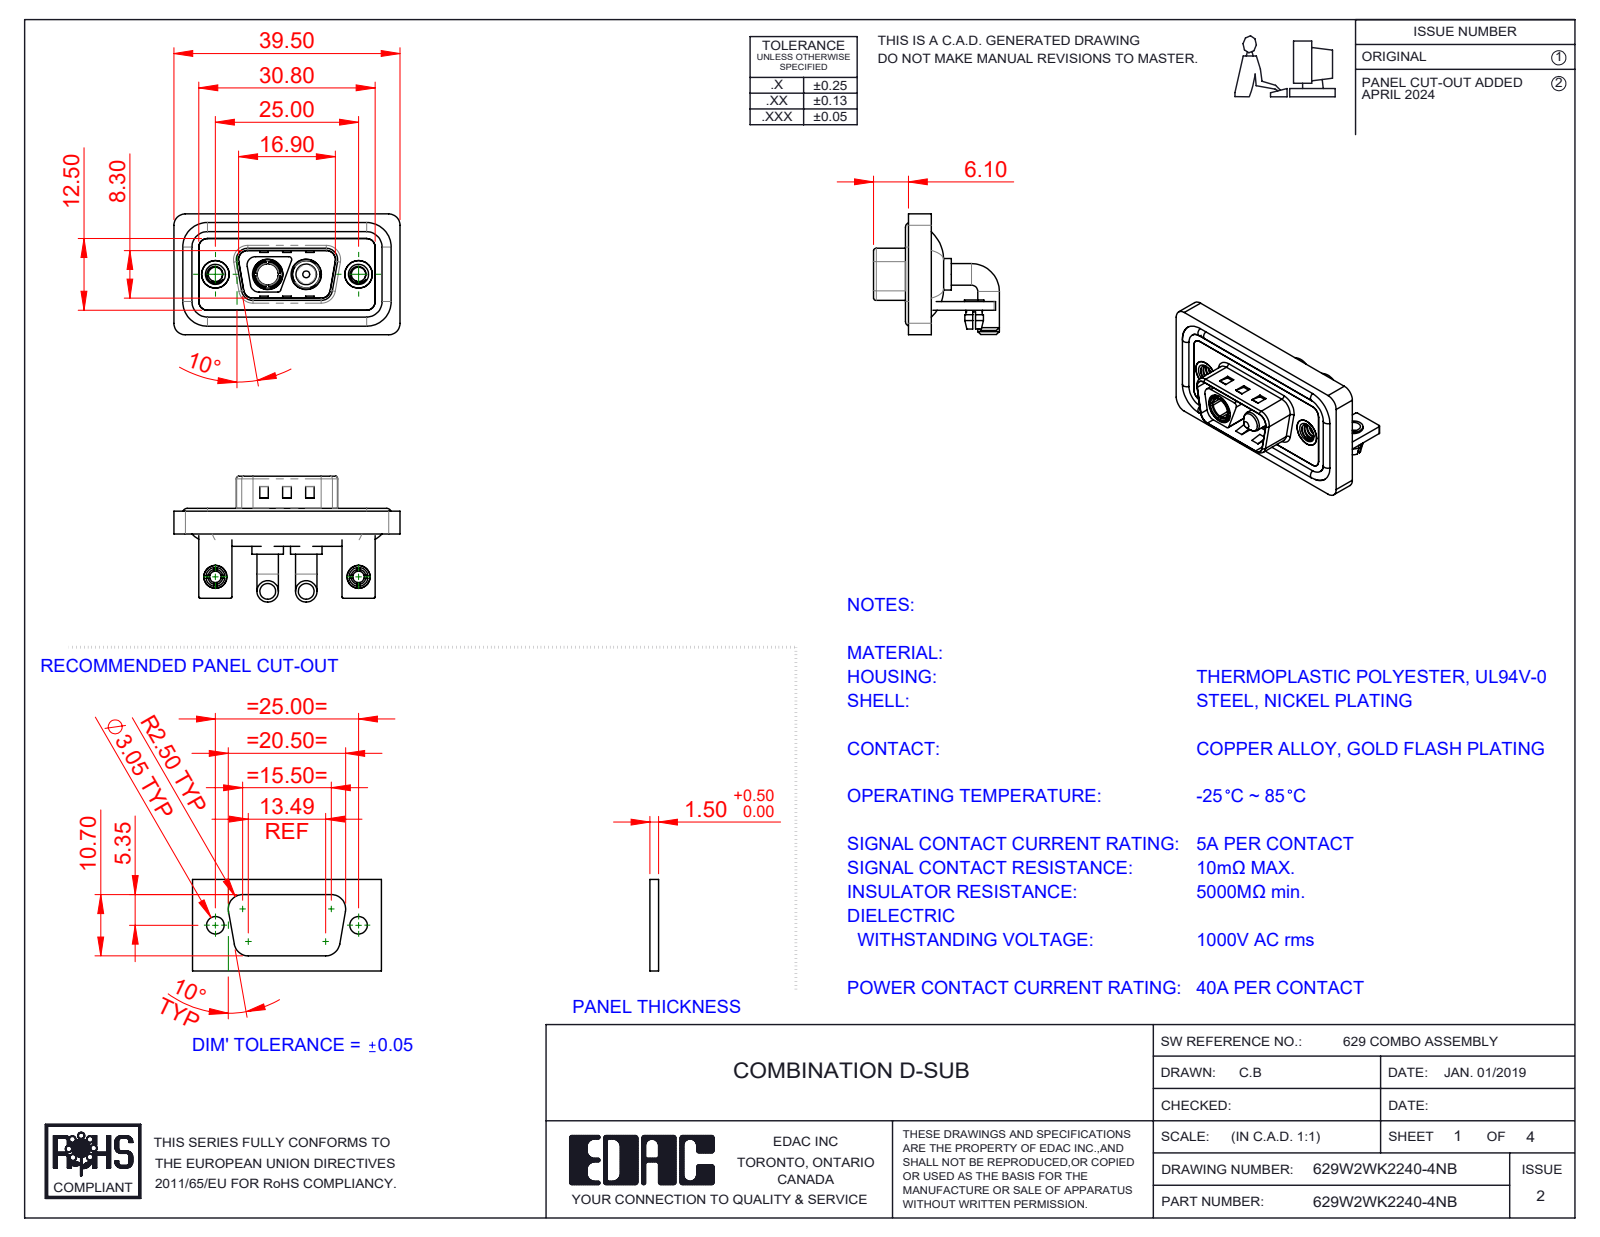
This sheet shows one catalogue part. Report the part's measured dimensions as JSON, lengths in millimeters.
{"part_name": "629Combo Shell Front_09 Contacts; 629Combo Waterproof Housing_09 Contacts; 629Combo Stabilizer Bracket; 629Combo Threaded Rivet_B (+6 more)", "step_written_by": "SolidWorks 2023 (CONFIG_CONTROL_DESIGN)", "units": "millimeters", "bodies": {"solids": 15, "faces": 672, "planar": 257, "cylindrical": 281, "other": 134}, "overall_size": [39.5, 21.98, 21.1], "volume_mm3": 5140, "surface_area_mm2": 8420, "round_holes": [[2.5, 4], [2, 2], [3.2, 2], [4, 2], [4.8, 2], [4.85, 2], [5, 2], [5.3, 2], [3.7, 1]], "round_bosses_or_shafts": [[3.75, 4], [1.6, 4], [5.5, 2], [5.2, 2], [4.9, 2], [4.75, 2], [4, 2], [3.4, 2]], "partial_cylinders_radius": [[1.5, 20], [2, 19], [0.25, 16], [0.5, 11], [1.6, 8], [0.6, 4], [0.65, 4], [0.9, 4]], "face_to_face_distances": [0.4, 1.5, 2.9, 0.8, 1.1, 1.2, 2.1, 1.6, 3.7, 2.5], "hole_center_spacings": [9.14, 15.86, 25, 6.72]}
